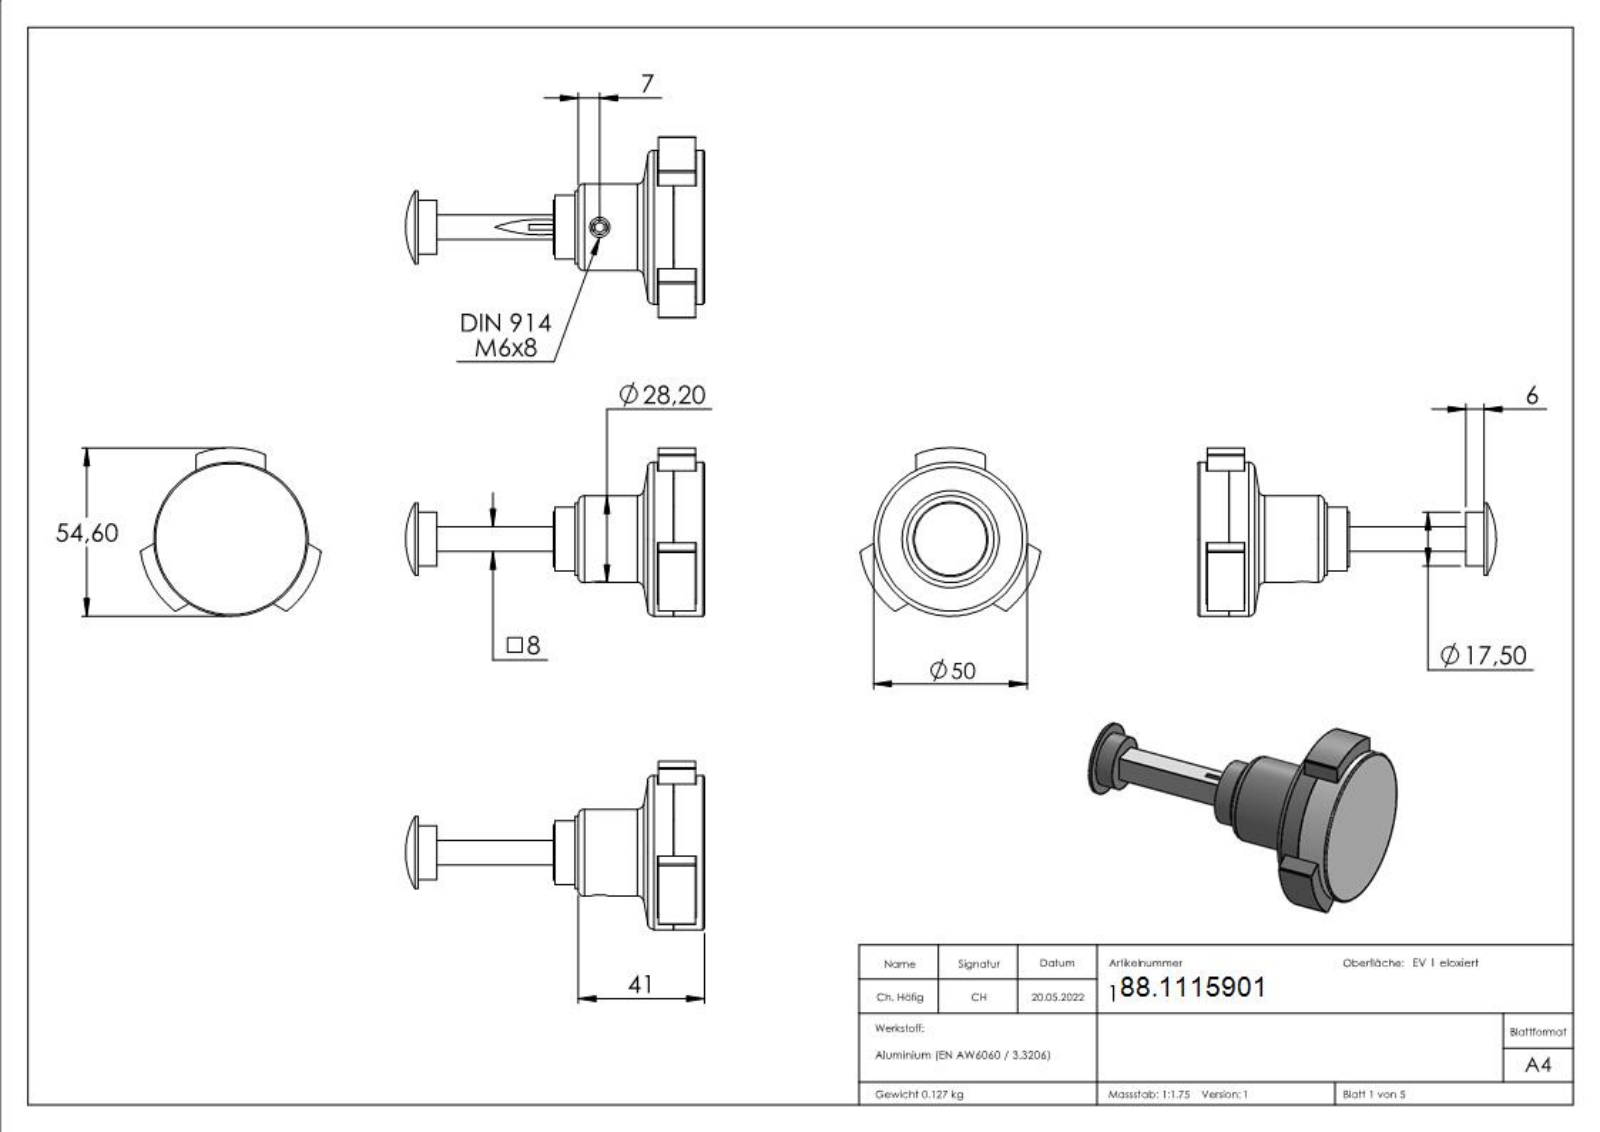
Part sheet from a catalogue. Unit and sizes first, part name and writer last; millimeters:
Units: millimetres
Overall size (bounding box): 97 × 58.59 × 54.6
Round holes (diameter × count): ⌀5 ×1, ⌀6.5 ×1, ⌀18.8 ×1, ⌀21.6 ×1
Round bosses / shafts (diameter × count): ⌀50 ×1, ⌀28.2 ×1, ⌀23.5 ×1, ⌀21.4 ×1, ⌀20.8 ×1, ⌀17.7 ×1, ⌀17.5 ×1, ⌀6 ×1
Partial cylindrical surfaces — rounded edges, fillets, slot ends (radius × count): R0.5 ×6, R0.25 ×4, R29.6 ×1
Main face-to-face distances: 8.1, 10, 10.1, 8, 7.15, 8.2, 12.25, 2.95, 12, 7.05
Volume: 59 336 mm³ · Surface area: 26 540 mm²
Bodies: 9 solids, 324 faces (190 planar, 27 cylindrical, 107 other)
Part name (STEP PRODUCT): 15901; 15901 Teil3_15901 Teil3; DIN914_DIN 914 M6x8; 15901 Teil2_15901 Teil2 (+1 more)
STEP written by: SolidWorks 2018 (CONFIG_CONTROL_DESIGN)
